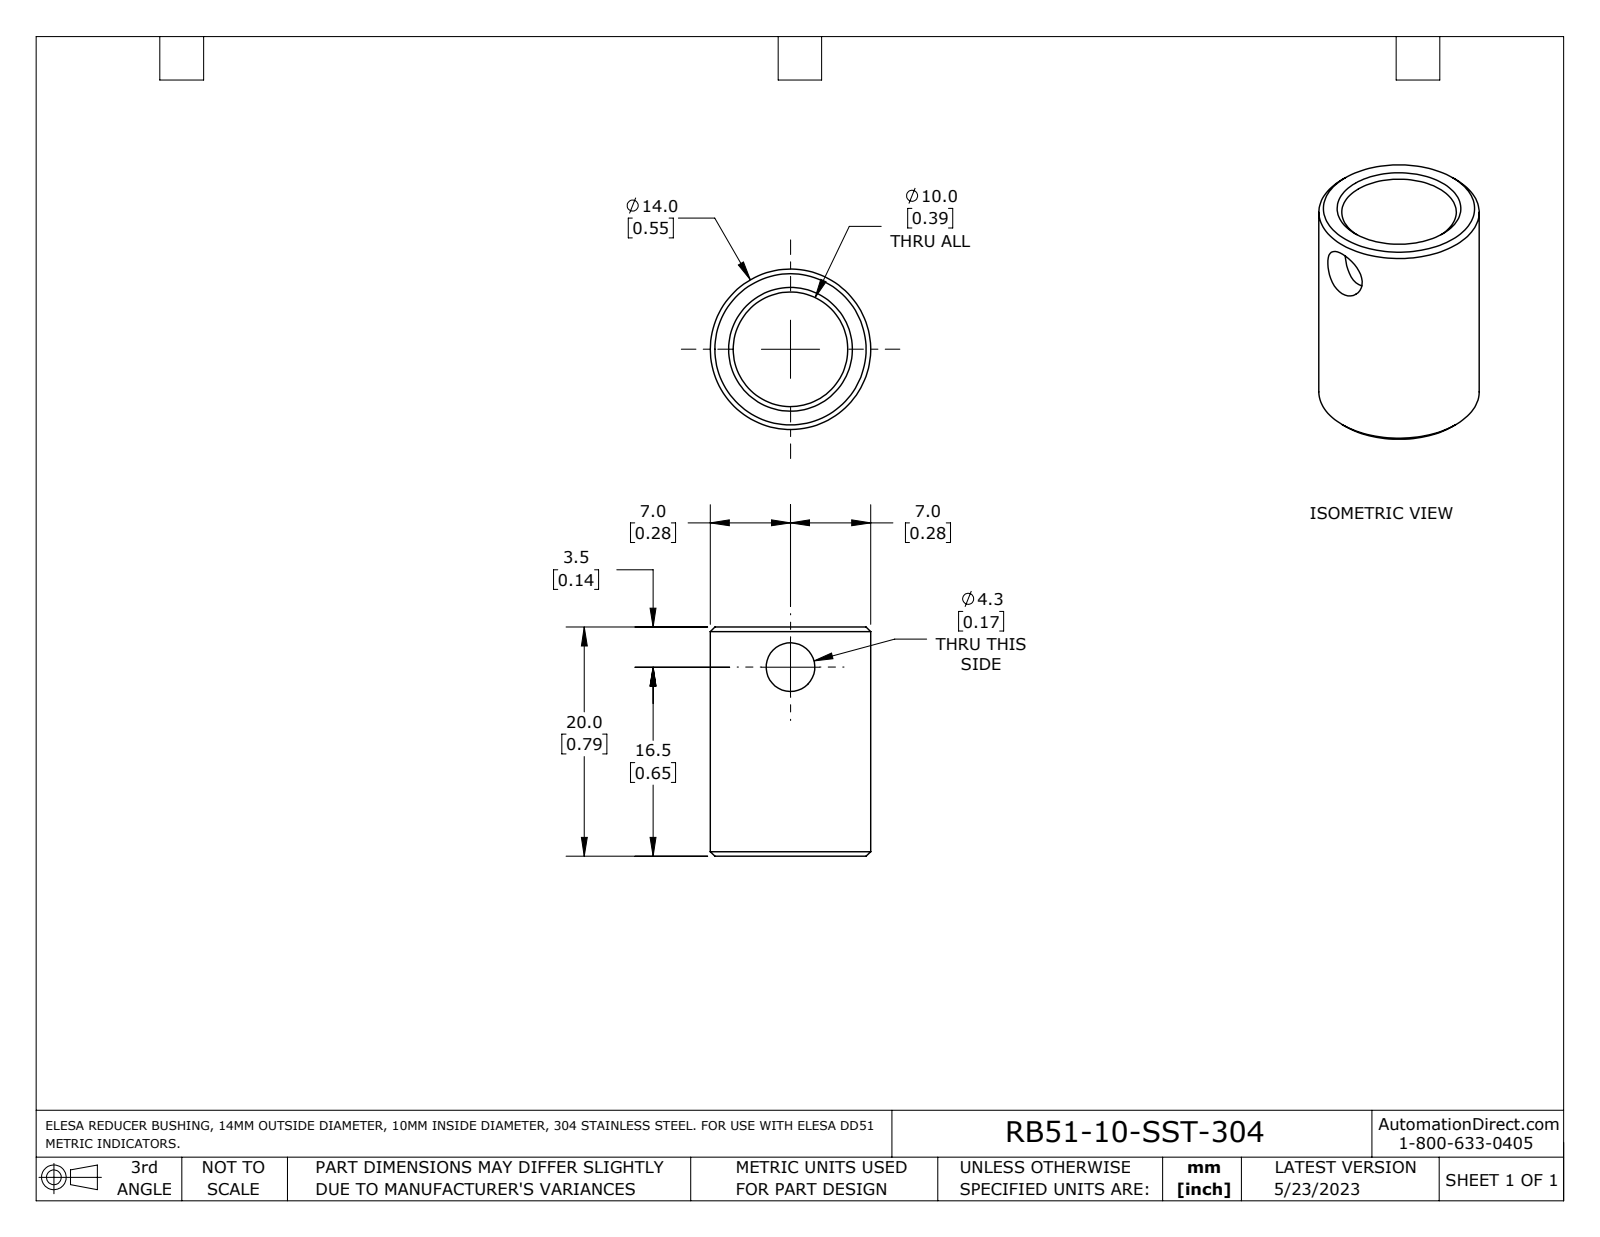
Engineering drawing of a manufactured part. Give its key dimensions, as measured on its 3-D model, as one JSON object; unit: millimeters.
{"part_name": "RB51-10-SST-304", "step_written_by": "SolidWorks 2021 (AUTOMOTIVE_DESIGN)", "units": "millimeters", "bodies": {"solids": 1, "faces": 9, "planar": 2, "cylindrical": 3, "other": 4}, "overall_size": [20, 14, 14], "volume_mm3": 1500, "surface_area_mm2": 1622, "round_holes": [[4.2, 1], [10, 1]], "round_bosses_or_shafts": [[14, 1]], "face_to_face_distances": [20]}
